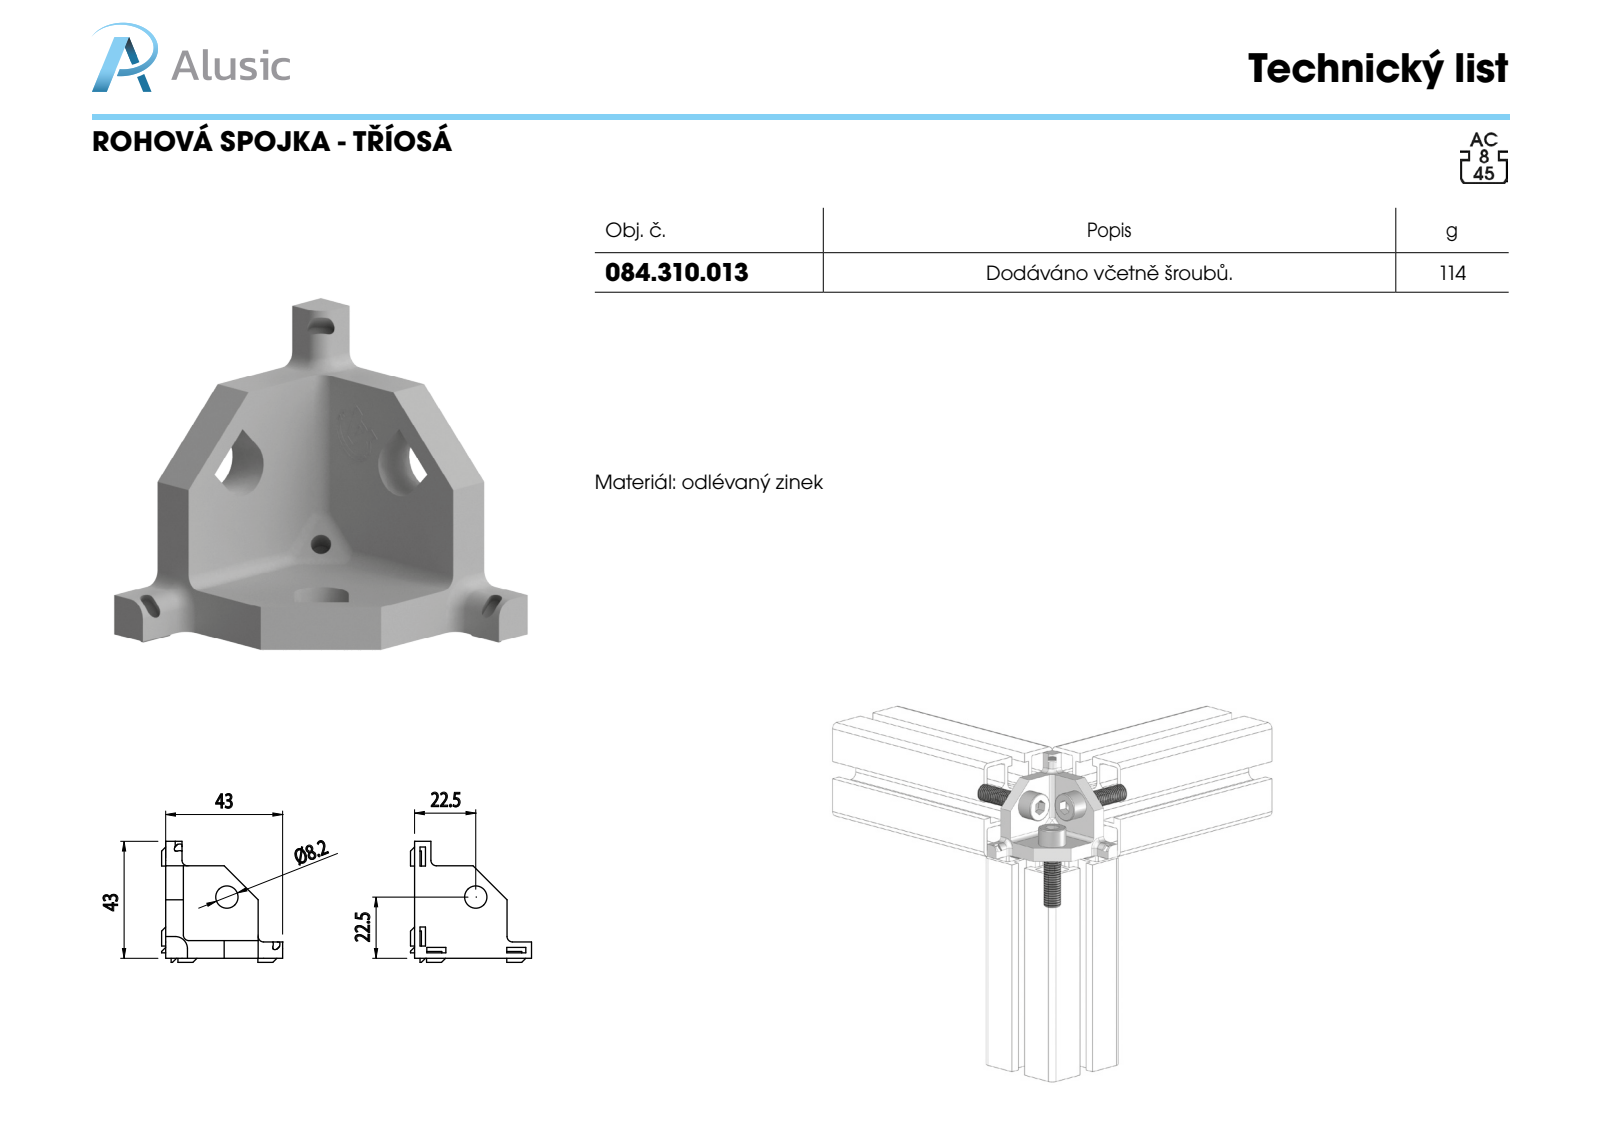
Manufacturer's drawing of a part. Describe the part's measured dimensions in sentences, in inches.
The part is named "084.310.013". Its 3-D file was written by "SolidWorks 2011 (CONFIG_CONTROL_DESIGN)". It is 0 solids with 128 faces: 92 planar, 24 cylindrical and 12 other. Overall it measures 1.752 by 1.752 by 1.752 inches. Round holes: 3 of diameter 0.323. Partial cylindrical surfaces (rounded edges, fillets, slot ends): 12 of radius 0.079, 3 of radius 0.098. The main face-to-face distances are 0.256, 1.339, 1.083, 0.236, 0.02, 1.102, 0.079, 1.693, 1.457, 1.437.
